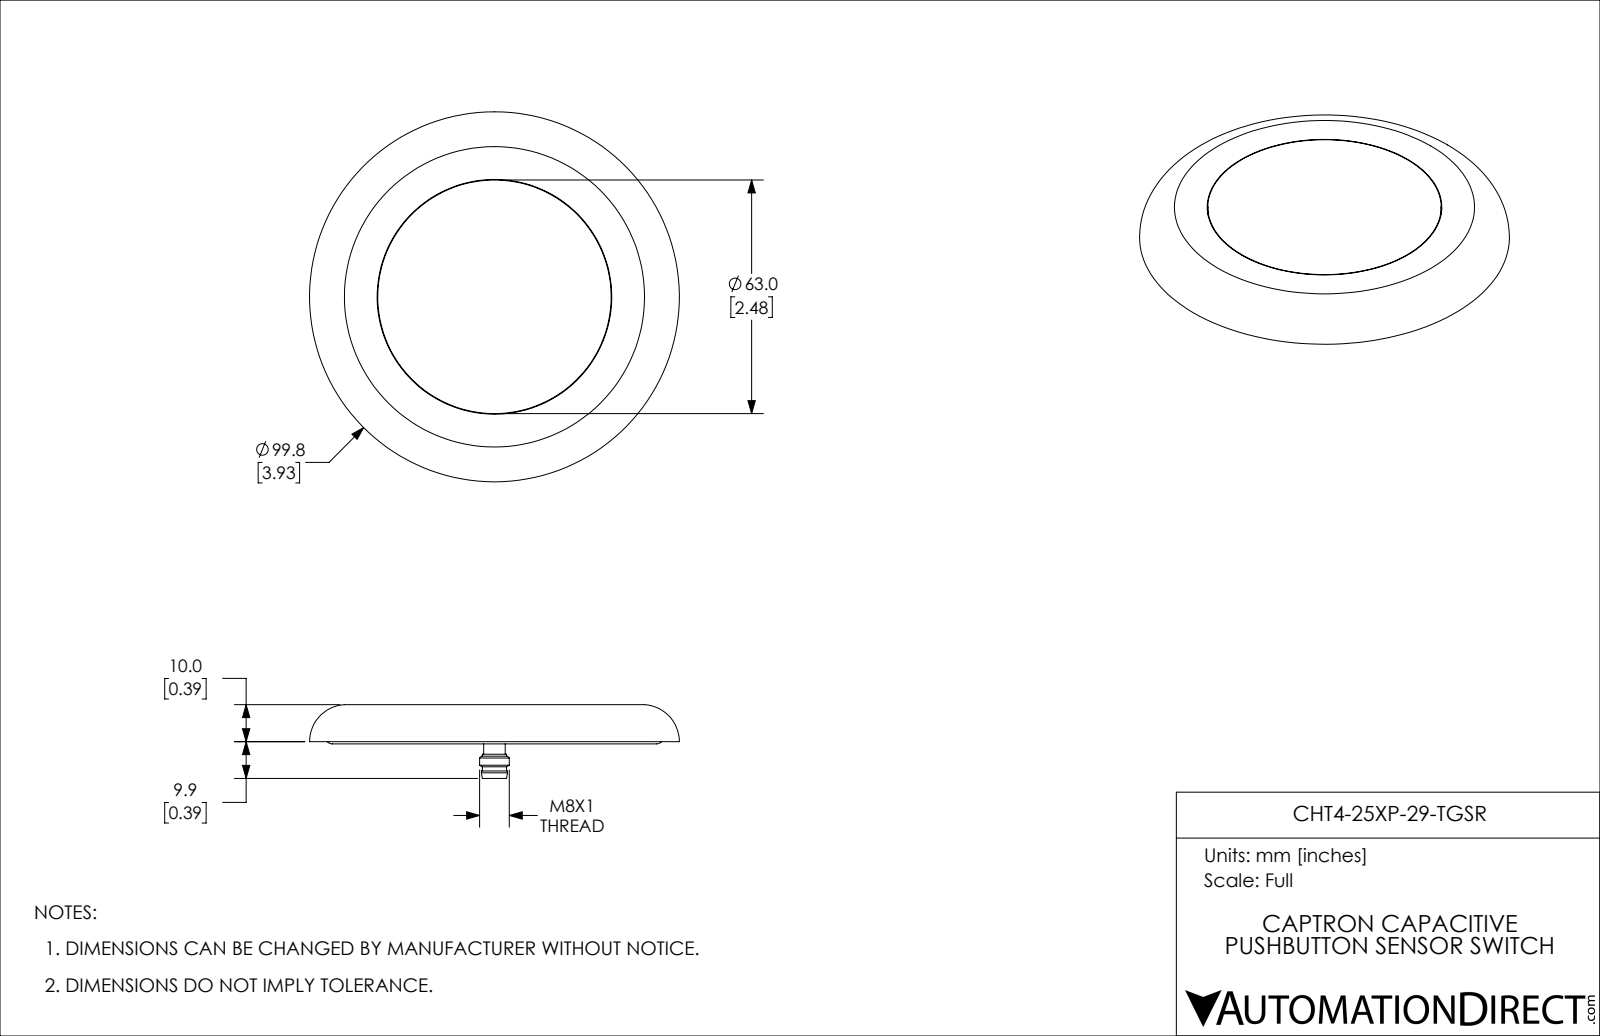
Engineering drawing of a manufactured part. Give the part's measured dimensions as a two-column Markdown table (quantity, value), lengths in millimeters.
| quantity | value |
| --- | --- |
| part name | CHT4-25XP-29-TGSR |
| STEP written by | SolidWorks 2019 (CONFIG_CONTROL_DESIGN) |
| units | millimeters |
| bodies | 13 solids, 102 faces (30 planar, 32 cylindrical, 40 other) |
| overall size | 99.8 × 99.8 × 19.9 |
| volume | 28 699 mm³ |
| surface area | 41 184 mm² |
| round holes (diameter × count) | 6 × 1, 58.4 × 1, 63.31 × 1, 64.6 × 1 |
| round bosses / shafts (diameter × count) | 1 × 4, 63 × 1, 8 × 1, 7 × 1, 6.5 × 1, 5.8 × 1 |
| partial cylindrical surfaces (radius × count) | 32 × 1 |
| main face-to-face distances | 8.28, 1.42, 9.7, 1.45, 8.24, 6.82, 1.46, 9.9, 1.62, 8.44 |
| hole center spacings | 3.19 |
